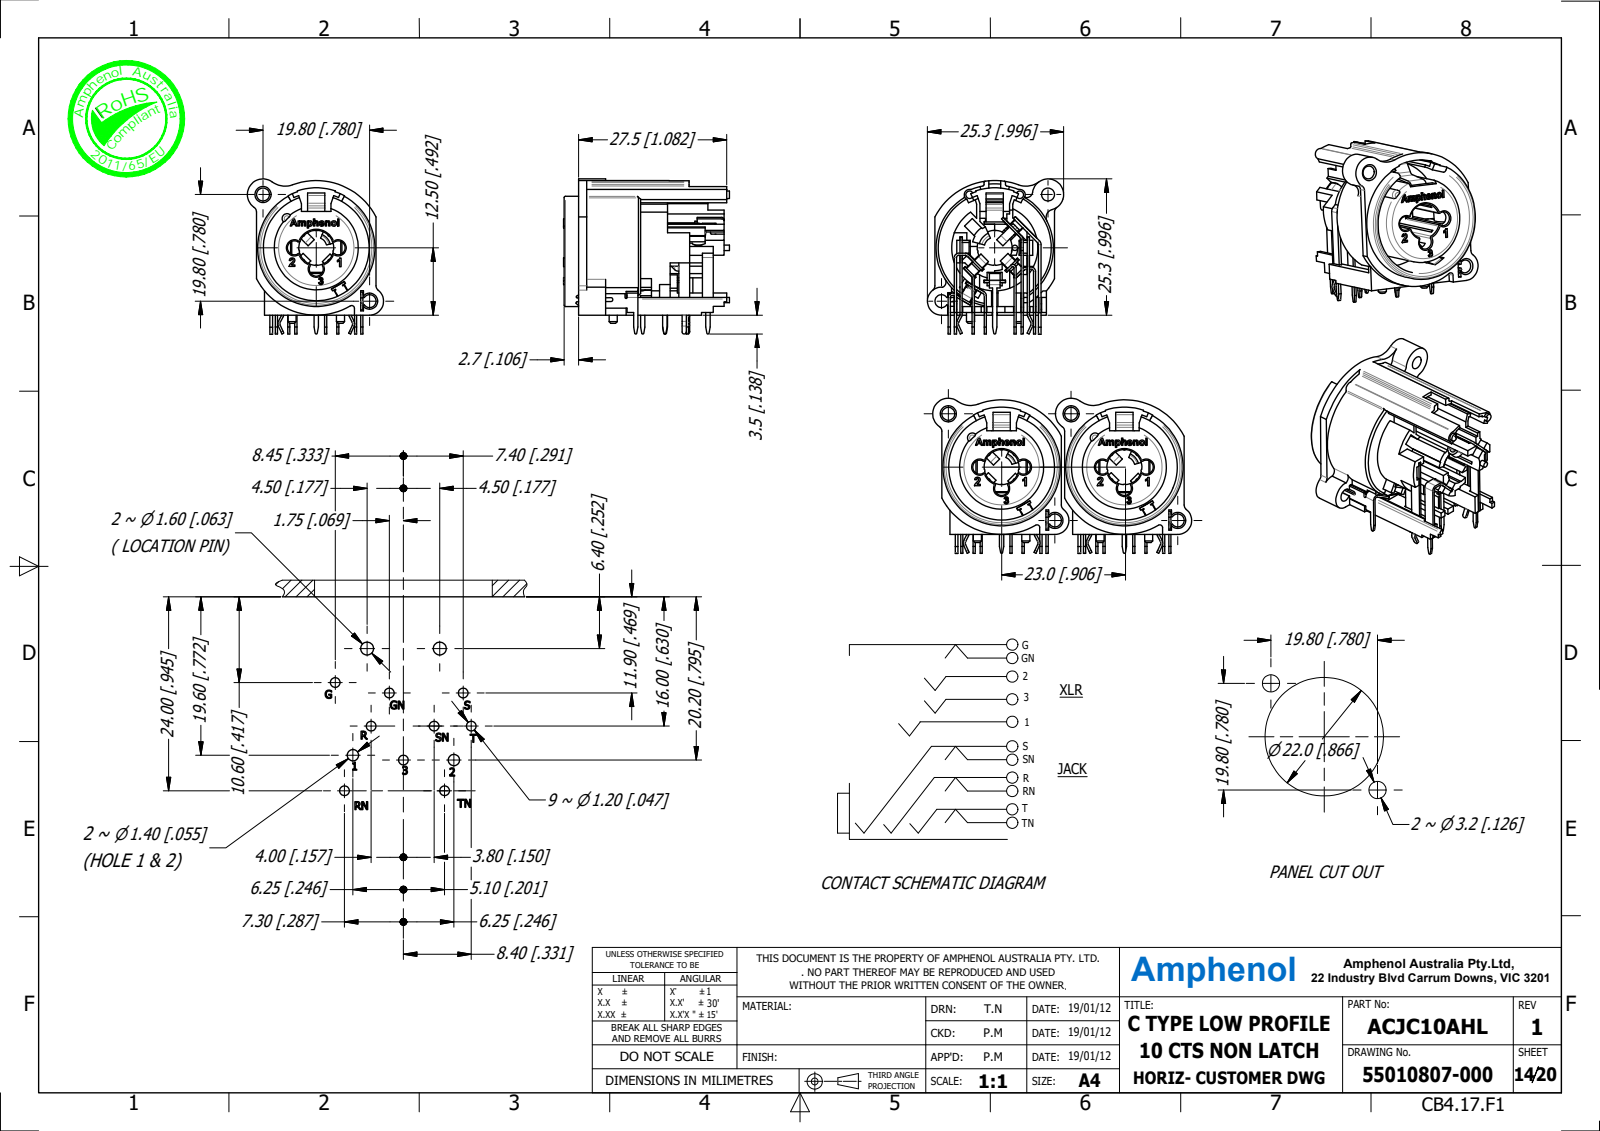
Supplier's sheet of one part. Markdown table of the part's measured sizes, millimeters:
| quantity | value |
| --- | --- |
| part name | ACJC10AHL; CT-PJ-21-HOUING; CT-PJ-21-TN; CT-PJ-21-1 (+8 more) |
| STEP written by | Autodesk Inventor 2018 (AP242_MANAGED_MODEL_BASED_3D_ENGINEERING_MIM_LF) |
| units | millimeters |
| bodies | 14 solids, 2108 faces (1588 planar, 368 cylindrical, 152 other) |
| overall size | 32.8 × 30 × 28.88 |
| volume | 5 060 mm³ |
| surface area | 11 733 mm² |
| round holes (diameter × count) | 1.2 × 9, 1.4 × 2, 1.6 × 2, 2 × 2, 2.4 × 2, 6.5 × 1, 19.5 × 1 |
| round bosses / shafts (diameter × count) | 1.5 × 2, 1.25 × 2, 21.8 × 1, 15.7 × 1, 1 × 1 |
| partial cylindrical surfaces (radius × count) | 0.15 × 84, 0.13 × 40, 0.2 × 37, 0.3 × 29, 0.5 × 22, 0.6 × 13, 0.9 × 12, 0.42 × 8 |
| main face-to-face distances | 0.4, 1, 0.42, 0.6, 2.1, 2.8, 2.2, 7.87, 13.1, 2 |
| hole center spacings | 8.28, 8.65, 12.4, 14, 14.52, 2.27, 3.97, 4.22 |
